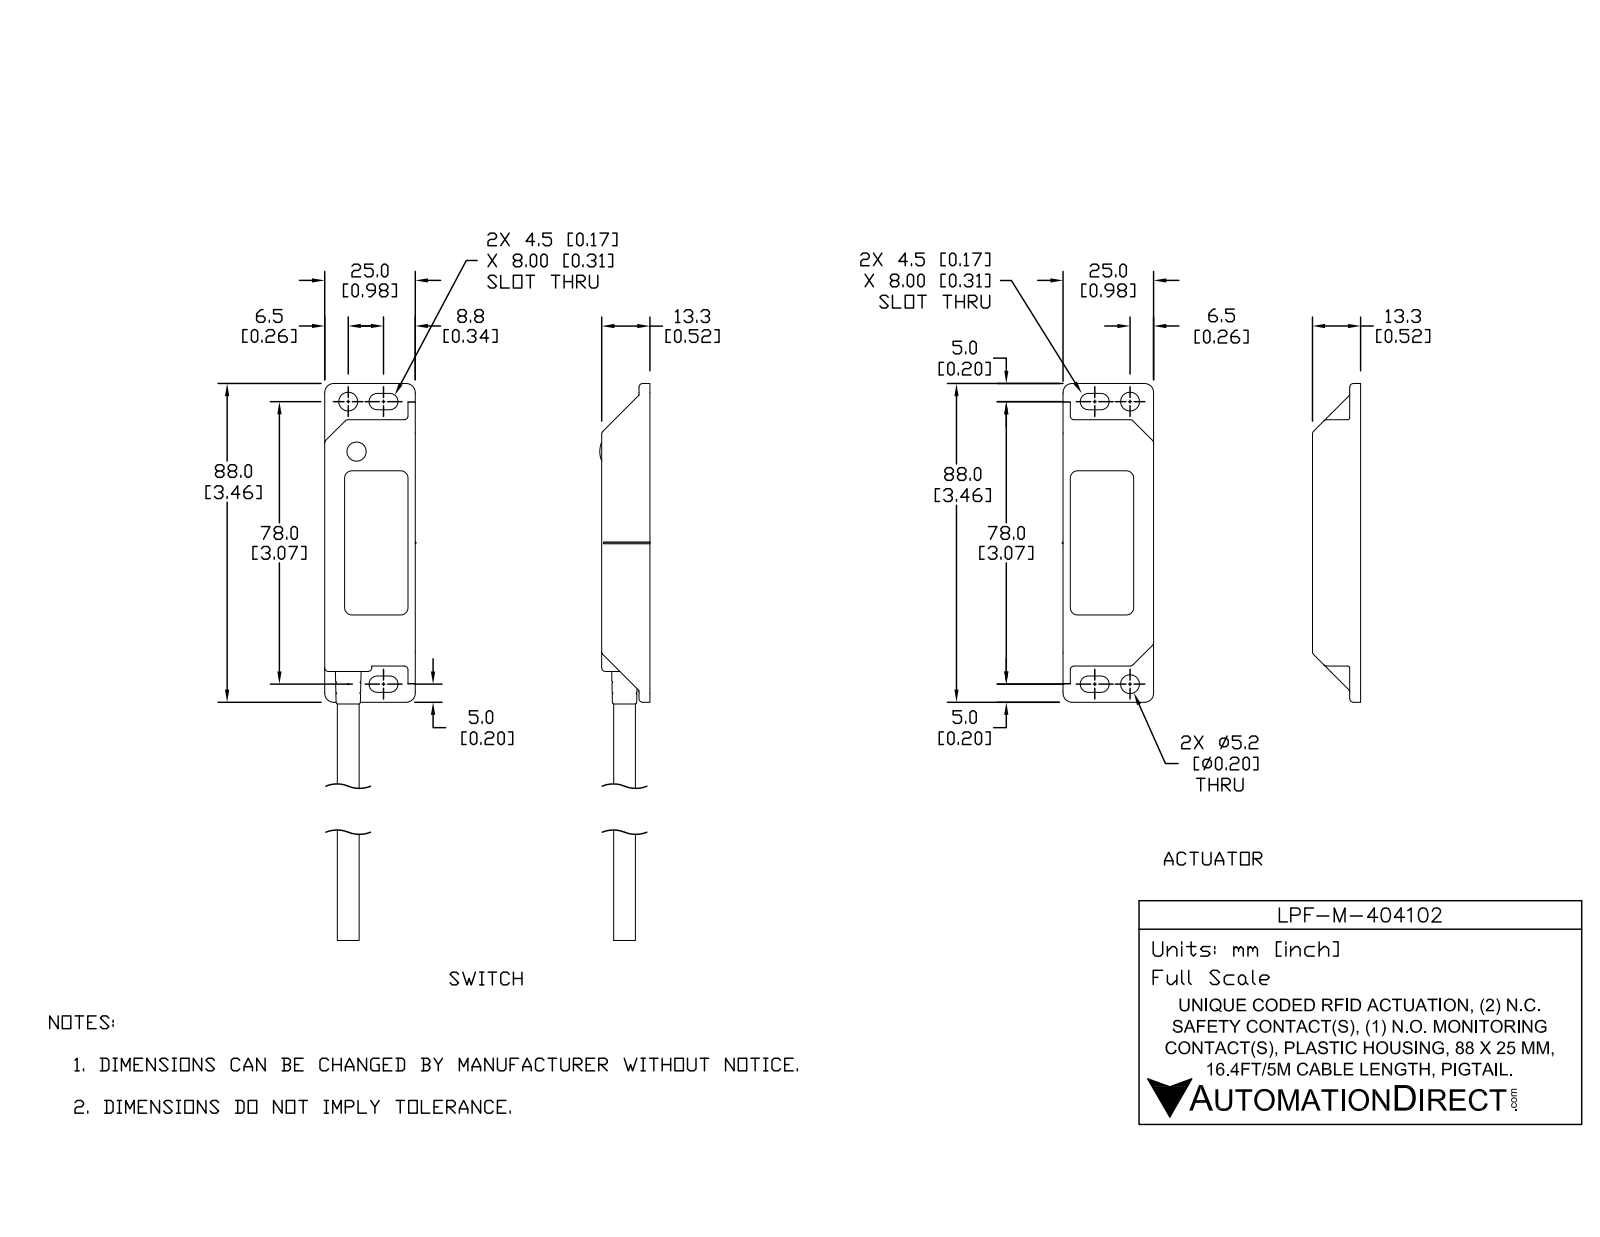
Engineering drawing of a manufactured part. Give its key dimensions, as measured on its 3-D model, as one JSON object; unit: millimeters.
{"part_name": "LPF-M-404102_1; LPF-M-404102; LPF-M-404102_2", "step_written_by": "SolidWorks 2017 (AUTOMOTIVE_DESIGN)", "units": "millimeters", "bodies": {"solids": 11, "faces": 1058, "planar": 401, "cylindrical": 303, "other": 354}, "overall_size": [224.8, 50.6, 13.8], "volume_mm3": 26840, "surface_area_mm2": 30250, "round_holes": [[5, 4], [5.2, 4], [3, 1], [4.4, 1], [5.4, 1], [5.9, 1], [7, 1]], "round_bosses_or_shafts": [[2, 4], [4.9, 2], [2.3, 2], [8.6, 1], [7.6, 1], [7.1, 1], [6, 1], [5.3, 1]], "partial_cylinders_radius": [[0.5, 116], [1, 49], [2, 10], [2.3, 8], [2.5, 8], [0.3, 6], [4.8, 1]], "face_to_face_distances": [1.7, 11.2, 2, 9.5, 1.5, 1.8, 12.9, 11.3, 13, 25.1], "hole_center_spacings": [19, 27.9, 30.2, 32.4, 37.6, 39.9, 45.3, 48.1]}
